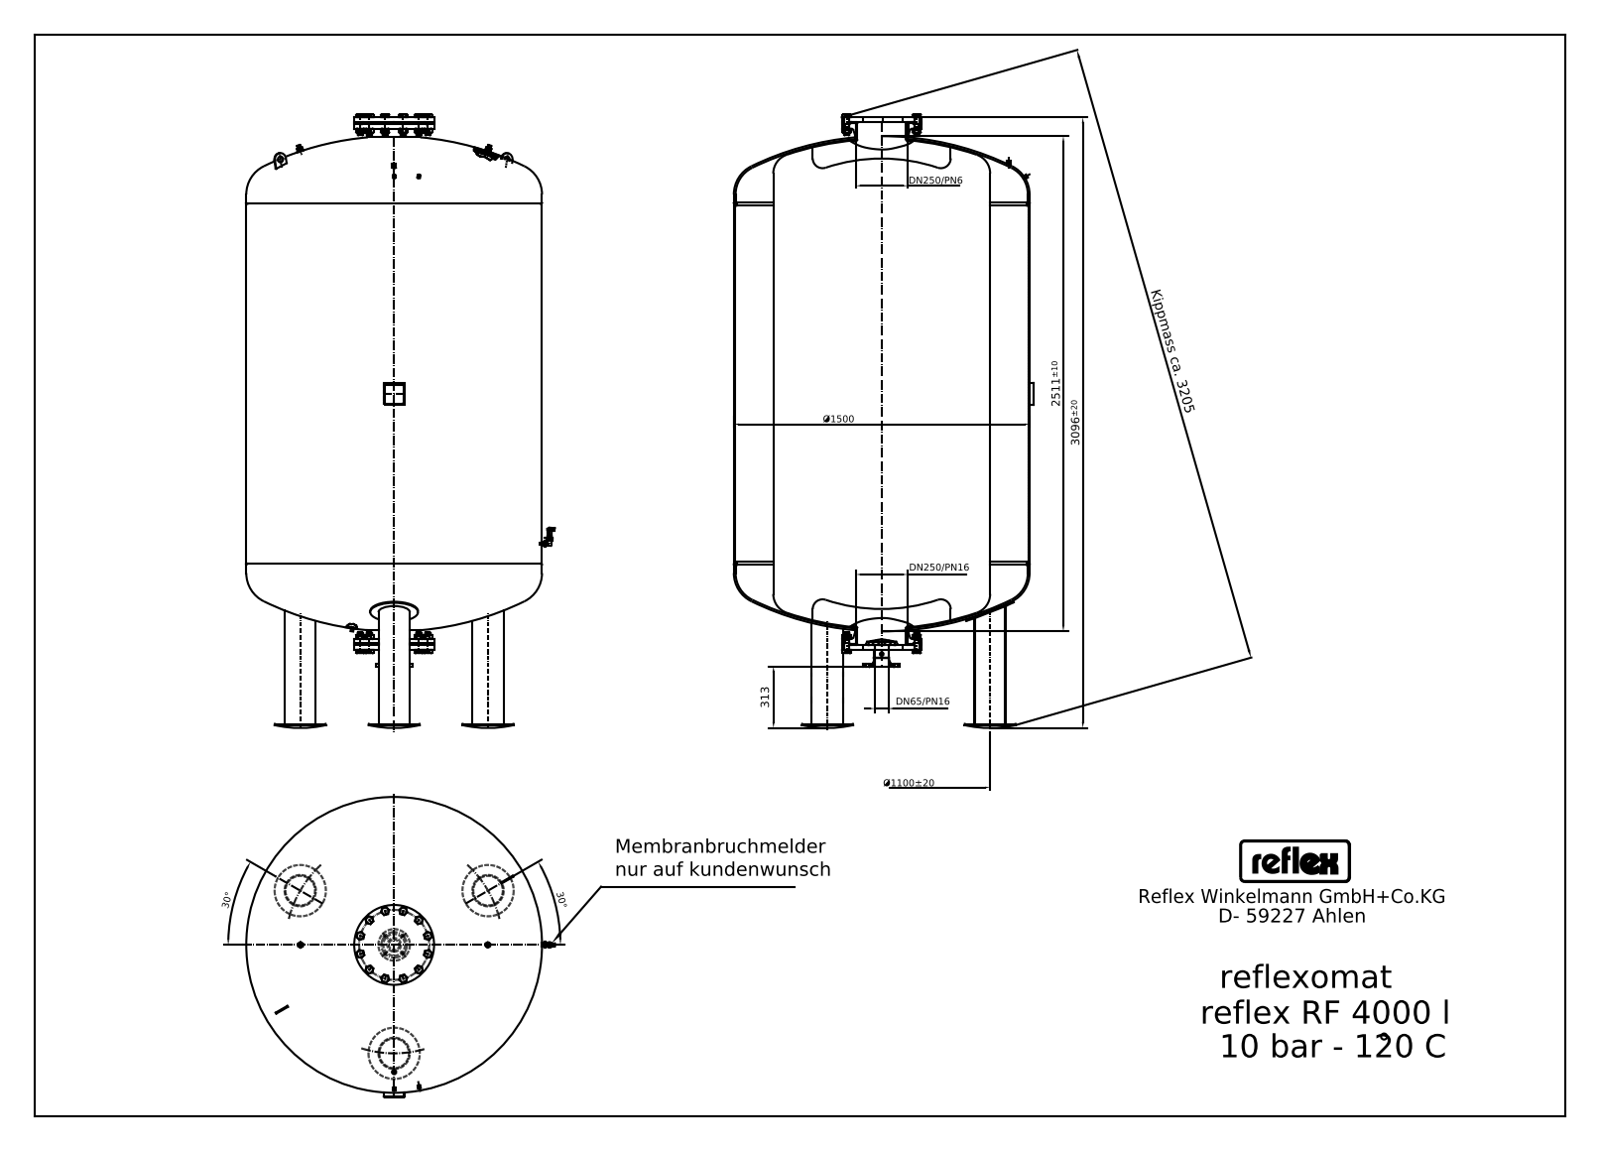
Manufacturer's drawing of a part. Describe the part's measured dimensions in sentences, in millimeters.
Its 3-D file was written by "Mechanical Desktop 2009 (CONFIG_CONTROL_DESIGN)". It is 23 solids with 889 faces: 514 planar, 207 cylindrical and 168 other. Overall it measures 3091 by 1566 by 1520 millimeters. Its volume is 4 124 000 000 cubic millimeters and its surface area 23 180 000 square millimeters. Round holes: 2 of diameter 11.45, 1 of diameter 3.5, 1 of diameter 14.95, 1 of diameter 30, 1 of diameter 260.4. Round bosses or shafts: 12 of diameter 16, 3 of diameter 159, 3 of diameter 21.3, 3 of diameter 18.5, 2 of diameter 28, 2 of diameter 20, 1 of diameter 1500, 1 of diameter 375. Partial cylindrical surfaces (rounded edges, fillets, slot ends): 5 of radius 1, 4 of radius 8.44, 3 of radius 3.38, 3 of radius 6, 2 of radius 2, 2 of radius 3, 2 of radius 5.76, 2 of radius 10.12. The main face-to-face distances are 1851, 22, 2668, 27, 2641, 2240, 389, 2262, 411, 428. The hole center spacings are 645, 769.5, 1004.07.
